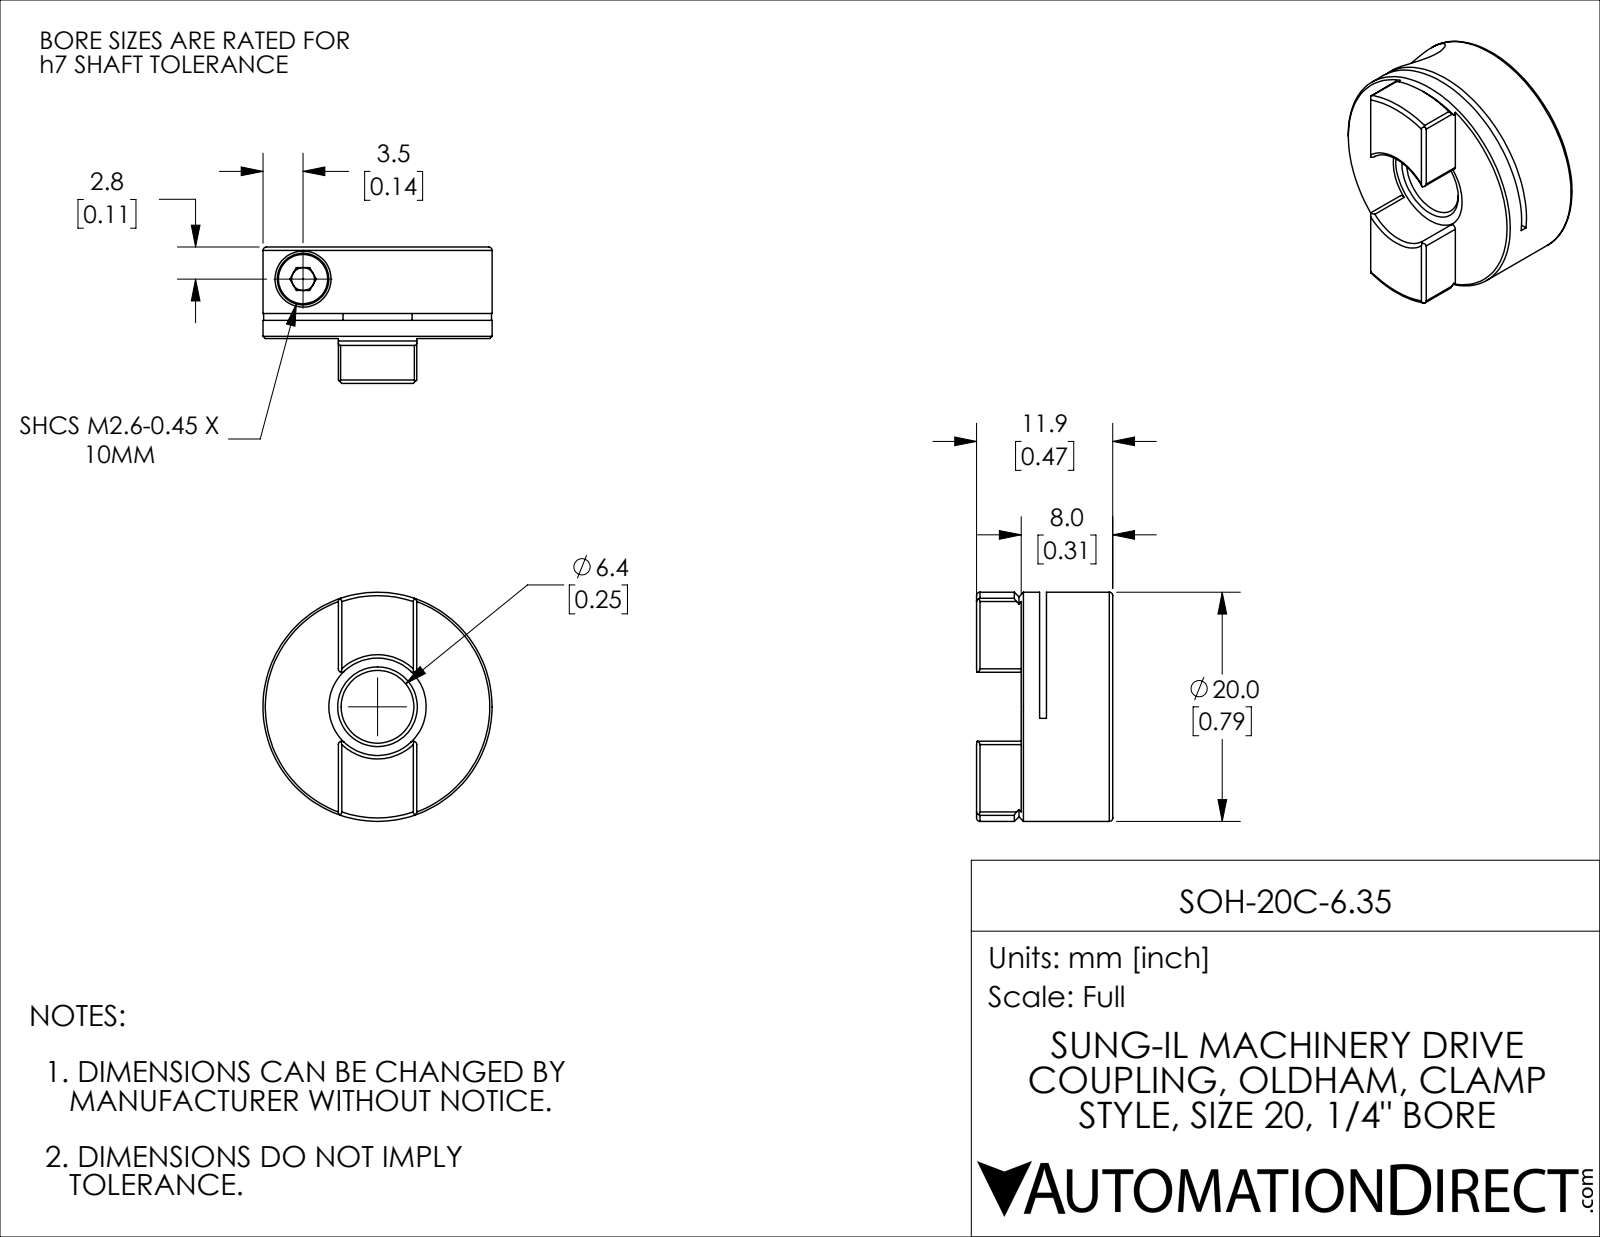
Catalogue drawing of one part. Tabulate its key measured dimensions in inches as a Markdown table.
| quantity | value |
| --- | --- |
| part name | SOH-20C-6 |
| STEP written by | SolidWorks 2021 (CONFIG_CONTROL_DESIGN) |
| units | inches |
| bodies | 2 solids, 97 faces (39 planar, 33 cylindrical, 25 other) |
| overall size | 0.787 × 0.787 × 0.469 |
| volume | 0.147 in³ |
| surface area | 3.184 in² |
| round holes (diameter × count) | 0.079 × 1, 0.081 × 1, 0.11 × 1, 0.193 × 1, 0.236 × 1, 0.335 × 1 |
| round bosses / shafts (diameter × count) | 0.787 × 1, 0.177 × 1, 0.102 × 1 |
| partial cylindrical surfaces (radius × count) | 0.012 × 8, 0.886 × 1 |
| main face-to-face distances | 0.315, 0.228, 0.252, 0.063, 0.024, 0.087, 0.154, 0.469, 0.24, 0.217 |
